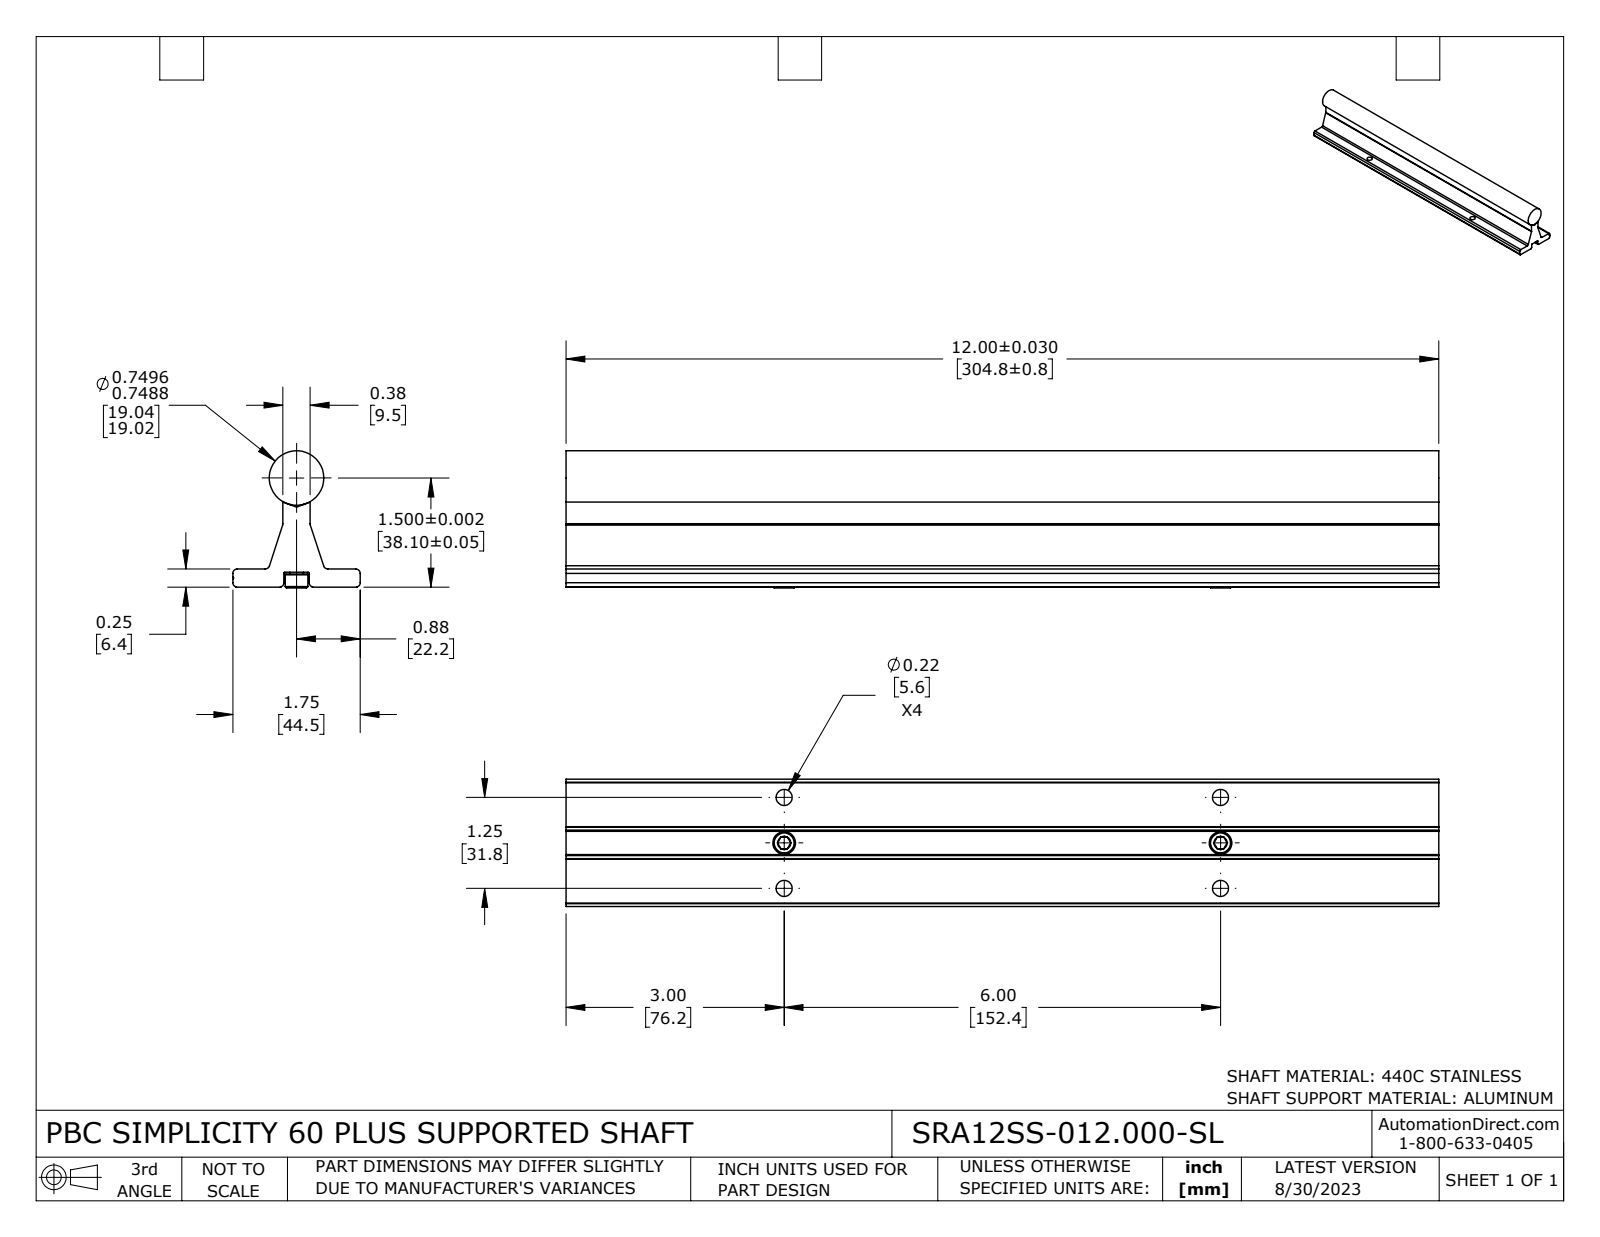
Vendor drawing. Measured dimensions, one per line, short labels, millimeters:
name: SRA12SS-012.000-SL
written by: SolidWorks 2021 (CONFIG_CONTROL_DESIGN)
unit: mm
bodies: 4 solids, 121 faces (49 planar, 42 cylindrical, 30 other)
size: 304.8 × 47.9 × 44.5
volume: 246 500 mm³; area: 67 290 mm²
holes: 6× ⌀5.6, 2× ⌀4.3, 2× ⌀6.4
bosses: 2× ⌀7.9, 2× ⌀4.8, 1× ⌀19.1
rounds: 6× R1.5, 2× R0.4, 2× R1.6, 2× R1.6
face distances: 6.4, 5.2, 1.1, 9.5, 0.3, 9.2, 17.5, 17.8, 26.7, 27
hole spacings: 15.9, 153.2, 152.4, 31.8, 155.7
